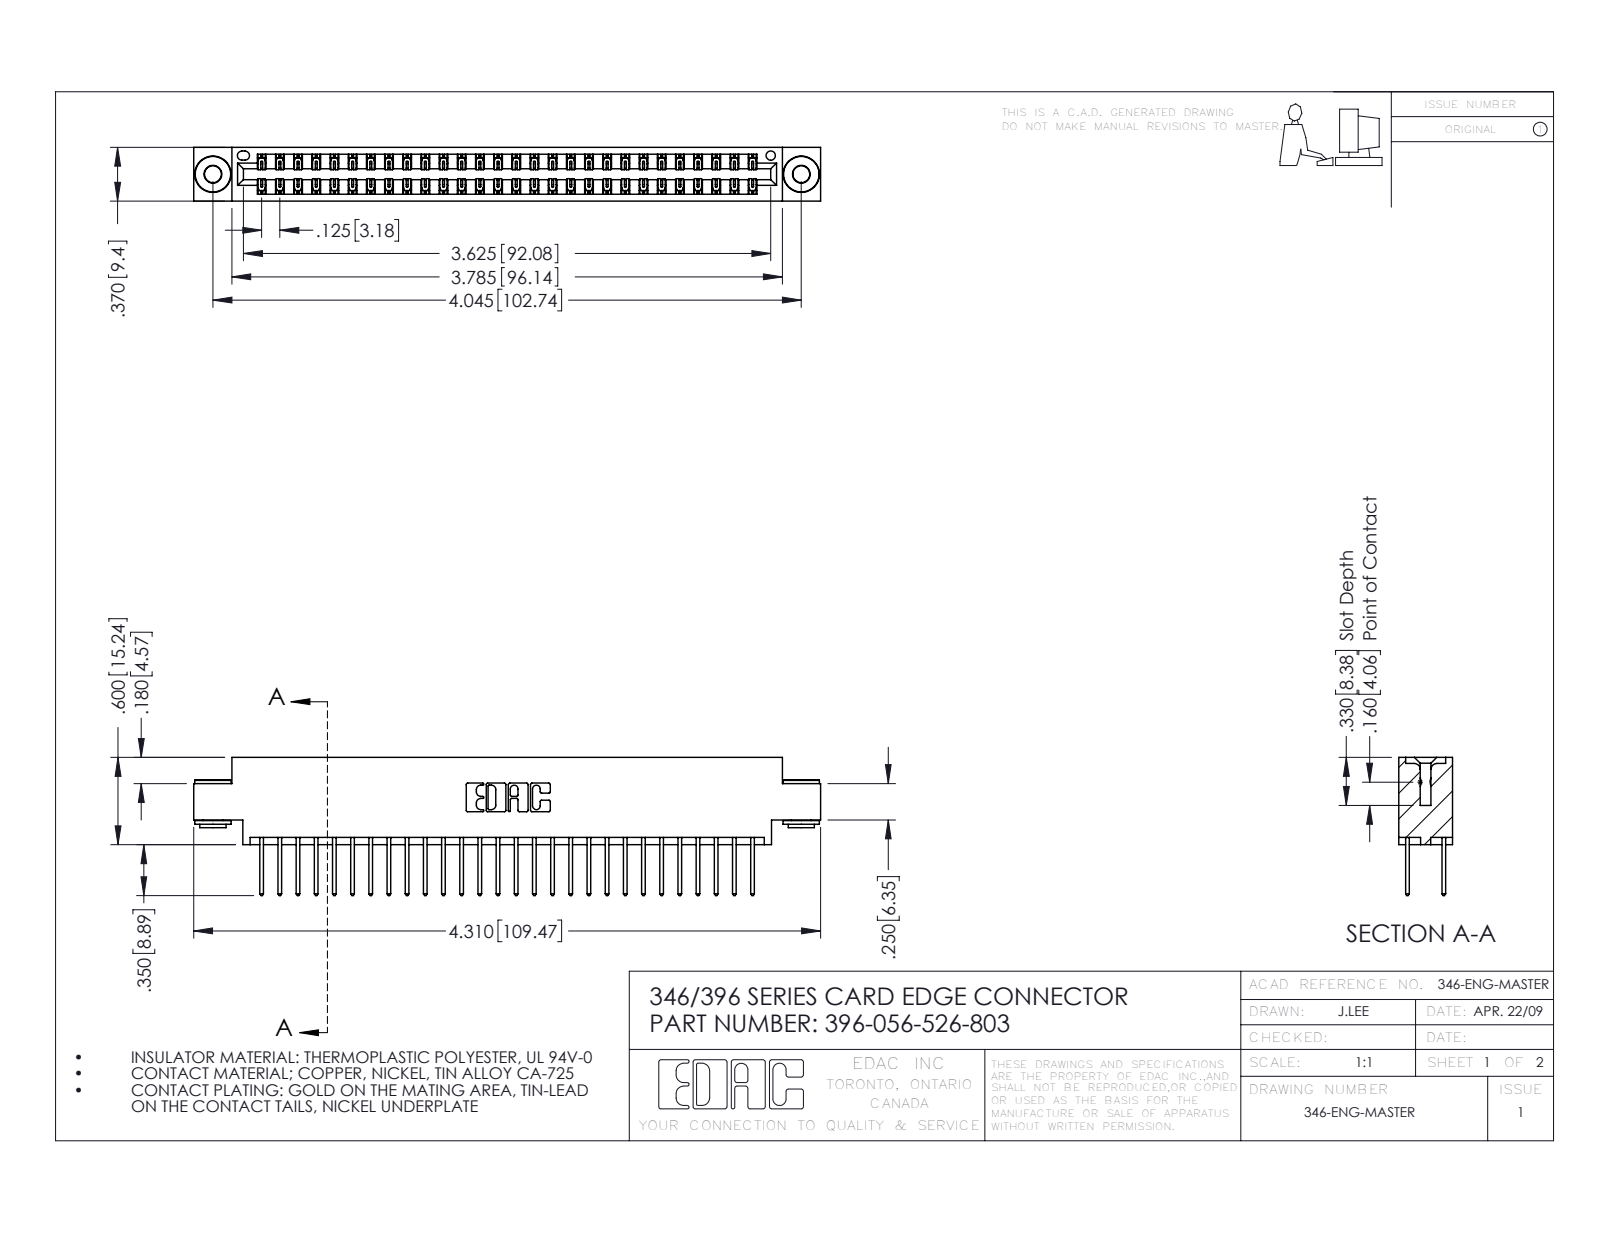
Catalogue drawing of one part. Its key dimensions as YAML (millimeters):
part_name: "345-292-001_345-293-126; 345-250-002_345-250-002-102; 346 Part_0.170 Offset - 0.156 Dia-TH; 396-056-526-803"
step_written_by: "SolidWorks 2016 (CONFIG_CONTROL_DESIGN)"
units: millimeters
bodies: {solids: 59, faces: 3076, planar: 2050, cylindrical: 1018, other: 8}
overall_size: [109.5, 24.1, 9.4]
volume: 10500
surface_area: 15050
round_holes:
  - {diameter: 2.9, count: 2}
  - {diameter: 4, count: 2}
  - {diameter: 1.6, count: 1}
round_bosses_or_shafts:
  - {diameter: 6.4, count: 2}
  - {diameter: 4.6, count: 2}
  - {diameter: 3.5, count: 2}
partial_cylinders:
  - {radius: 0.2, count: 84}
  - {radius: 0.3, count: 56}
  - {radius: 0.3, count: 22}
  - {radius: 0.2, count: 6}
  - {radius: 0.8, count: 6}
  - {radius: 0.7, count: 3}
  - {radius: 0.4, count: 2}
  - {radius: 0.6, count: 2}
face_to_face_distances: [1.2, 8.2, 6.4, 9.4, 0.6, 1.8, 7.6, 7, 3.8, 5.6]
hole_center_spacings: [6.2, 97.5, 102.7]
